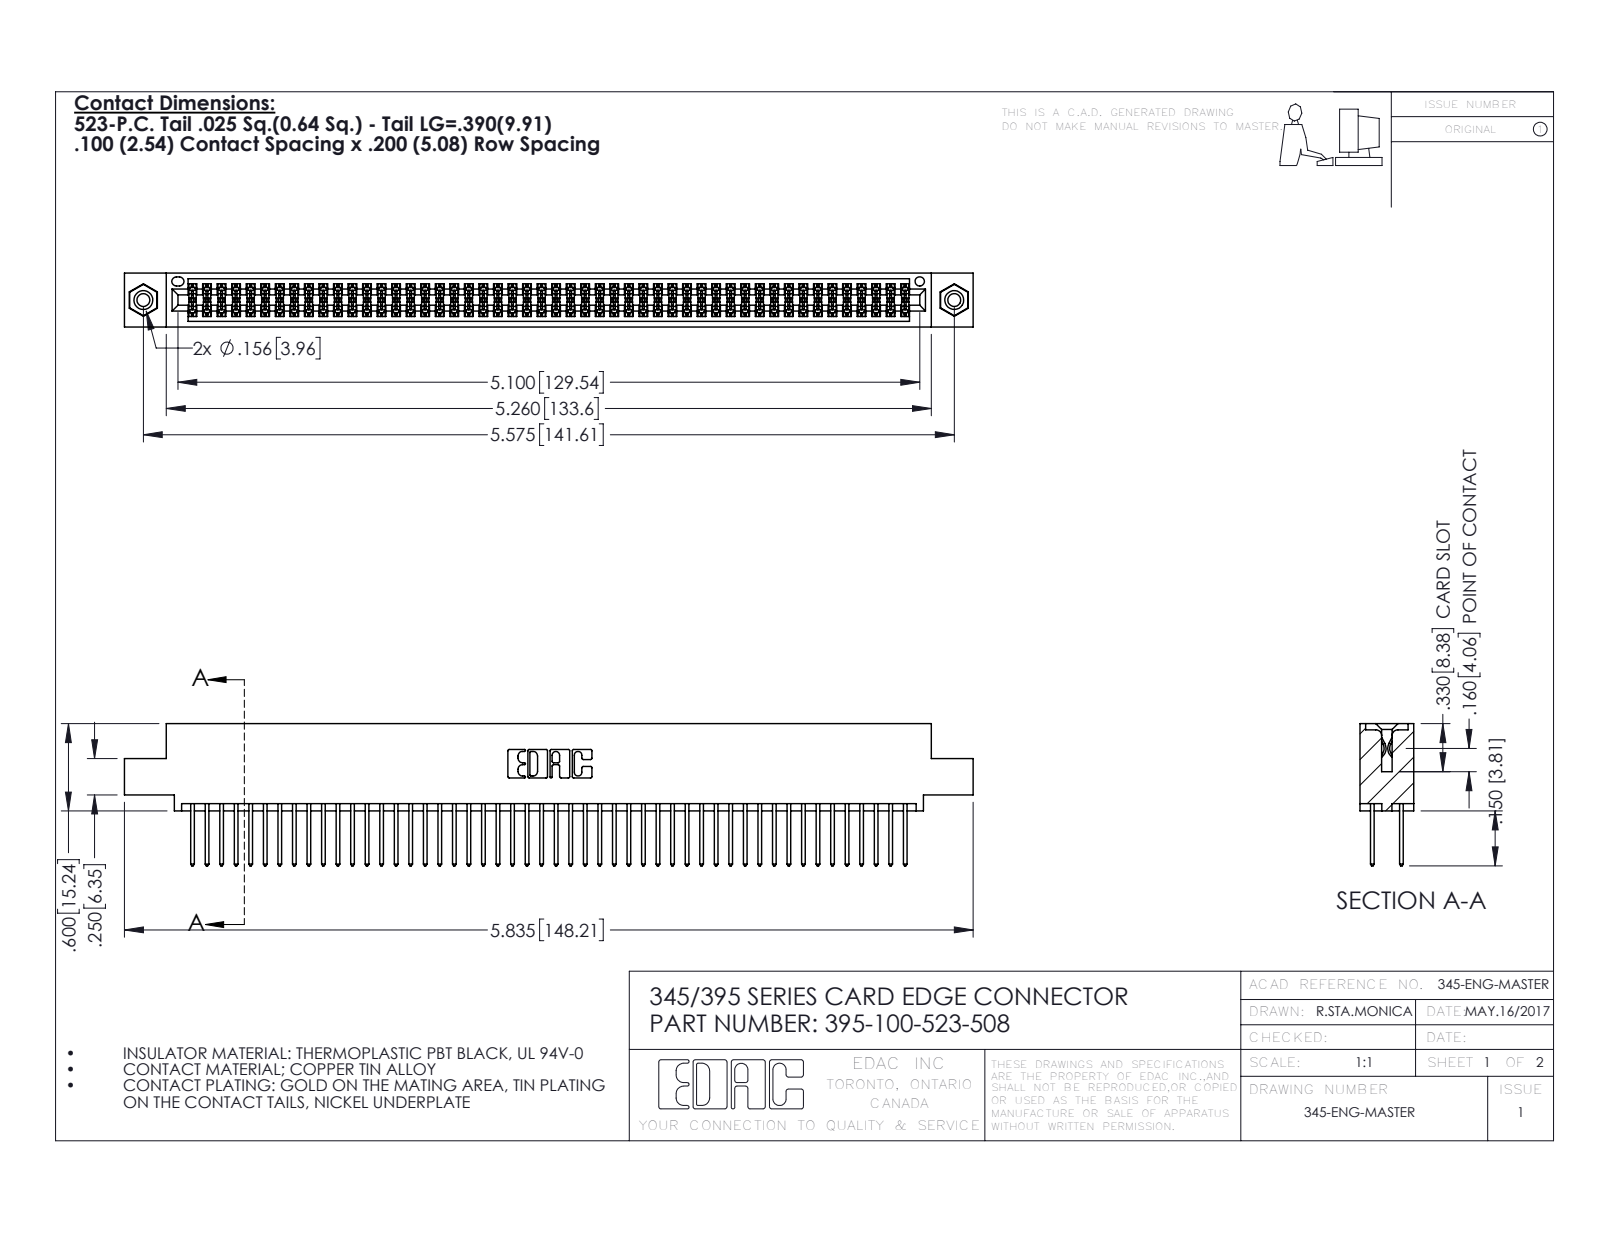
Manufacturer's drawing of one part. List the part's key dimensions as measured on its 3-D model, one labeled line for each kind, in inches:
Part name (STEP PRODUCT): 395-100-523-508; 345 Part_0.110 Offset - 0.156 Dia-TI; 345-292-001_345-293-123; 345-250-001_345-250-003-102
STEP written by: SolidWorks 2016 (CONFIG_CONTROL_DESIGN)
Units: inches
Bodies: 103 solids, 5190 faces (3416 planar, 1758 cylindrical, 16 other)
Overall size (bounding box): 5.835 × 0.977 × 0.37
Volume: 0.891 in³ · Surface area: 35.27 in²
Round holes (diameter × count): ⌀0.089 ×2, ⌀0.125 ×2, ⌀0.156 ×2, ⌀0.064 ×1
Round bosses / shafts (diameter × count): ⌀0.155 ×2
Partial cylindrical surfaces — rounded edges, fillets, slot ends (radius × count): R0.006 ×150, R0.01 ×100, R0.01 ×22, R0.007 ×6, R0.031 ×6, R0.026 ×3, R0.014 ×2, R0.019 ×2
Main face-to-face distances: 0.072, 0.298, 0.2, 0.098, 0.272, 0.025, 0.37, 0.225, 0.175, 0.149
Hole centre spacings: 0.27, 5.339, 5.575
